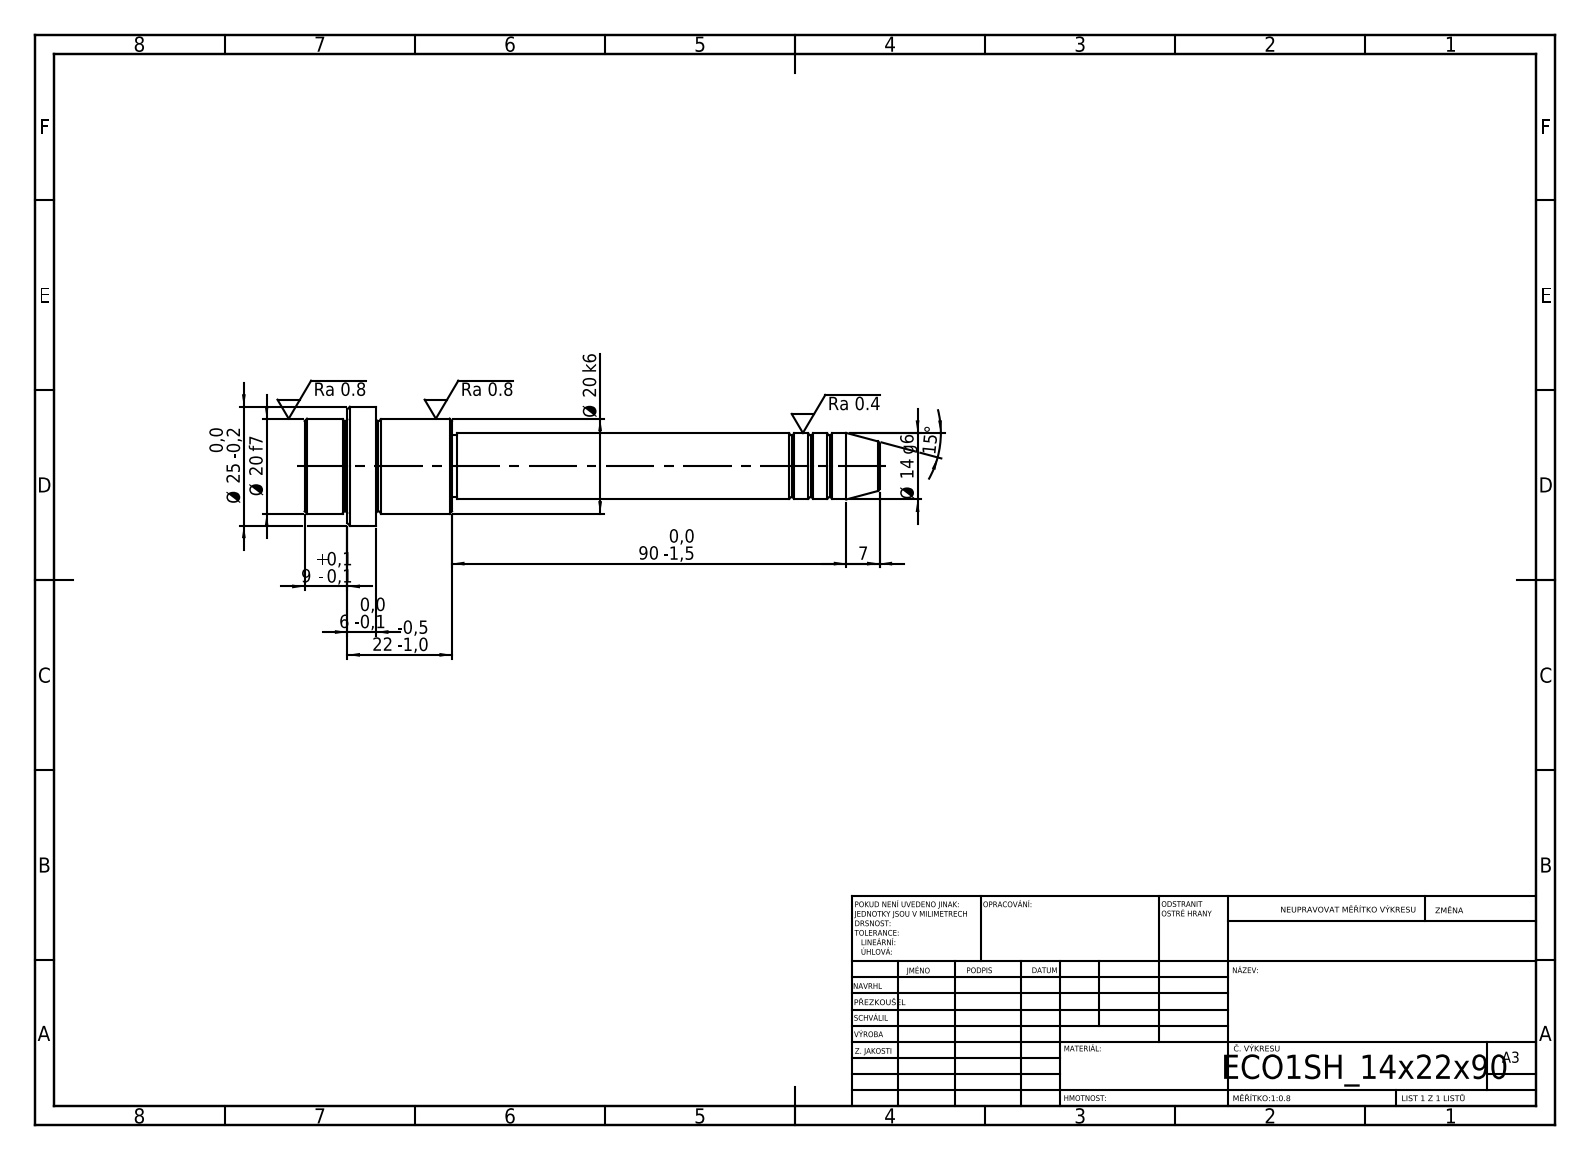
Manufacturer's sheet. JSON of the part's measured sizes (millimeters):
{"step_written_by": "SolidWorks 2019 (CONFIG_CONTROL_DESIGN)", "units": "millimeters", "bodies": {"solids": 1, "faces": 52, "planar": 6, "cylindrical": 16, "other": 30}, "overall_size": [121, 25, 25], "volume_mm3": 24245, "surface_area_mm2": 6985, "round_bosses_or_shafts": [[25, 1], [20, 1], [14, 1], [13, 1]], "face_to_face_distances": [15, 16, 31, 22, 6, 9, 90, 106, 112, 121]}
